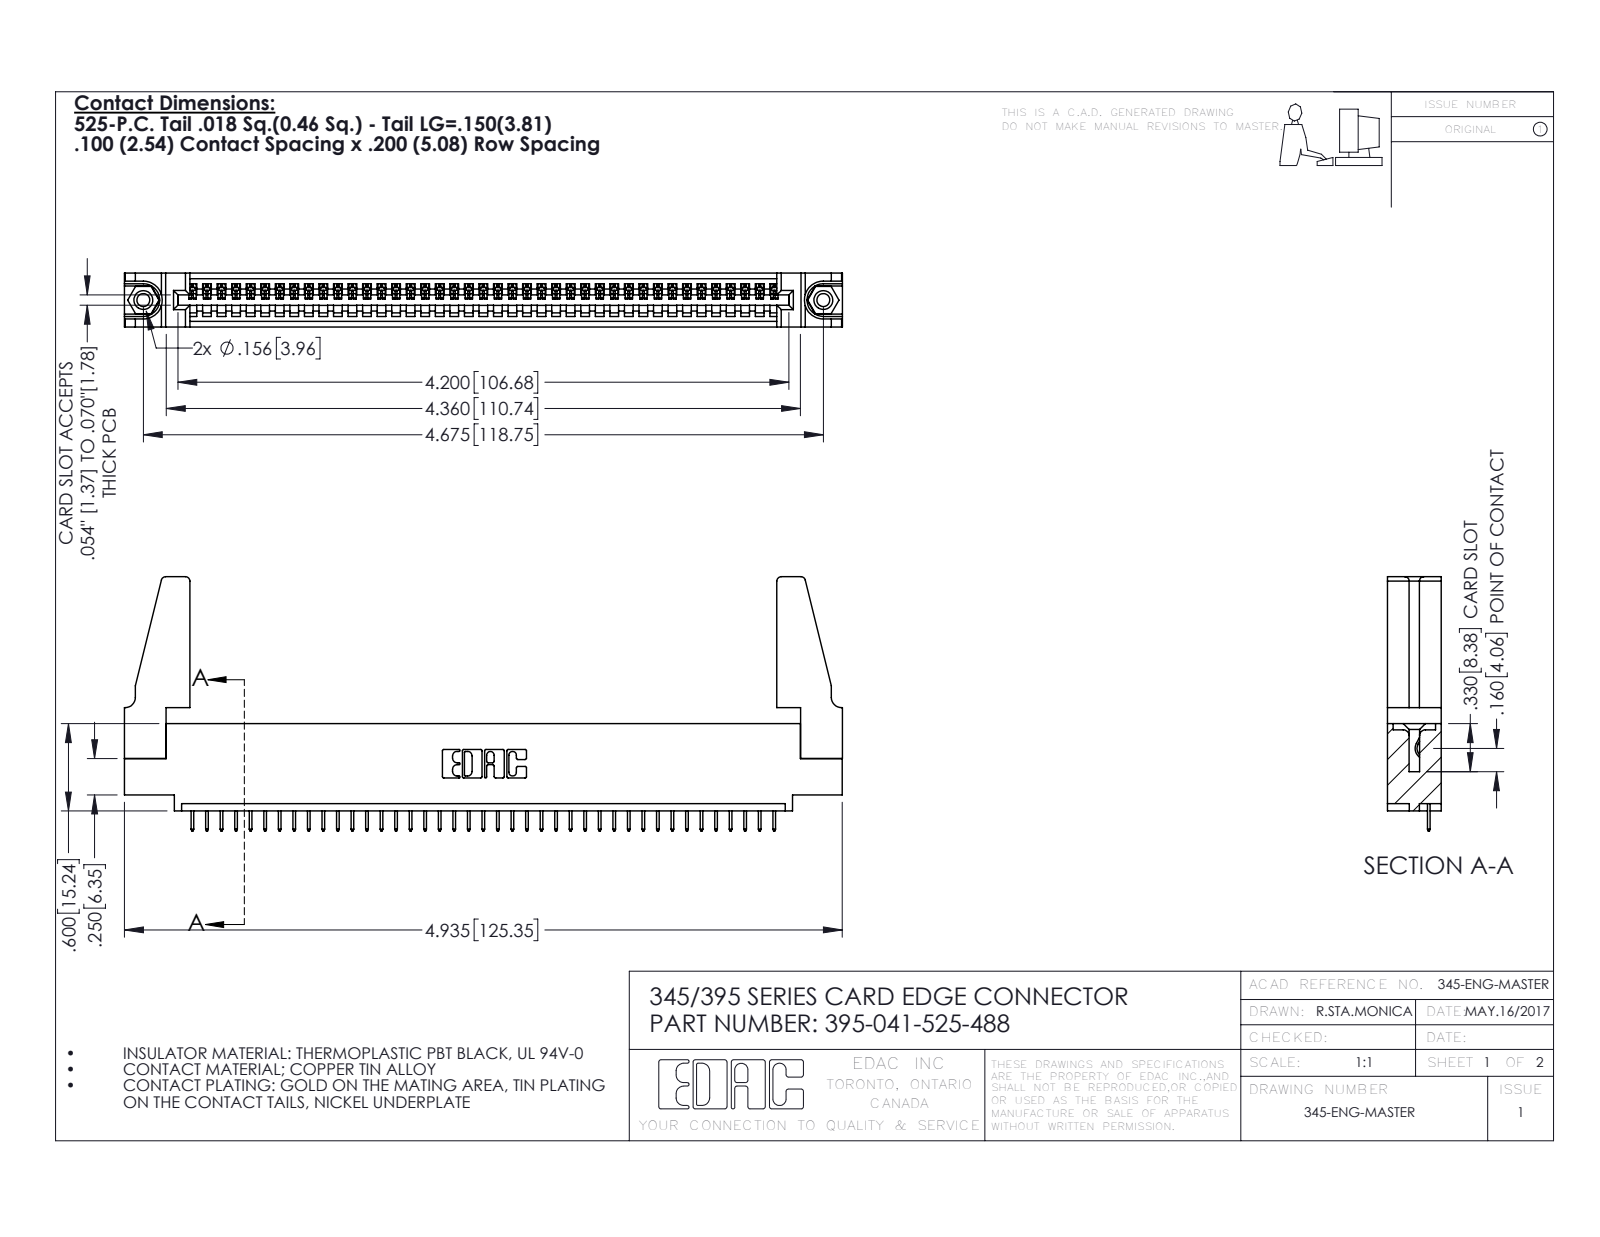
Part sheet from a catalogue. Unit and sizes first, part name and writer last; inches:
Units: inches
Overall size (bounding box): 4.936 × 1.747 × 0.37
Round holes (diameter × count): ⌀0.089 ×2, ⌀0.125 ×2, ⌀0.156 ×2, ⌀0.064 ×1
Round bosses / shafts (diameter × count): ⌀0.155 ×2
Partial cylindrical surfaces — rounded edges, fillets, slot ends (radius × count): R0.006 ×82, R0.01 ×22, R0.03 ×8, R0.007 ×6, R0.031 ×6, R0.026 ×3, R0.031 ×2, R0.04 ×2
Main face-to-face distances: 0.072, 0.37, 0.298, 0.2, 0.098, 0.272, 0.025, 0.225, 0.072, 0.149
Hole centre spacings: 0.27, 4.439, 4.675
Volume: 0.91 in³ · Surface area: 28.11 in²
Bodies: 46 solids, 2796 faces (2042 planar, 738 cylindrical, 16 other)
Part name (STEP PRODUCT): 395-041-525-488; 345-220-078_345-220-088; 345-292-001_345-293-125; 345 Part_0.110 Offset - 0.156 Dia-TH (+1 more)
STEP written by: SolidWorks 2020 (CONFIG_CONTROL_DESIGN)
